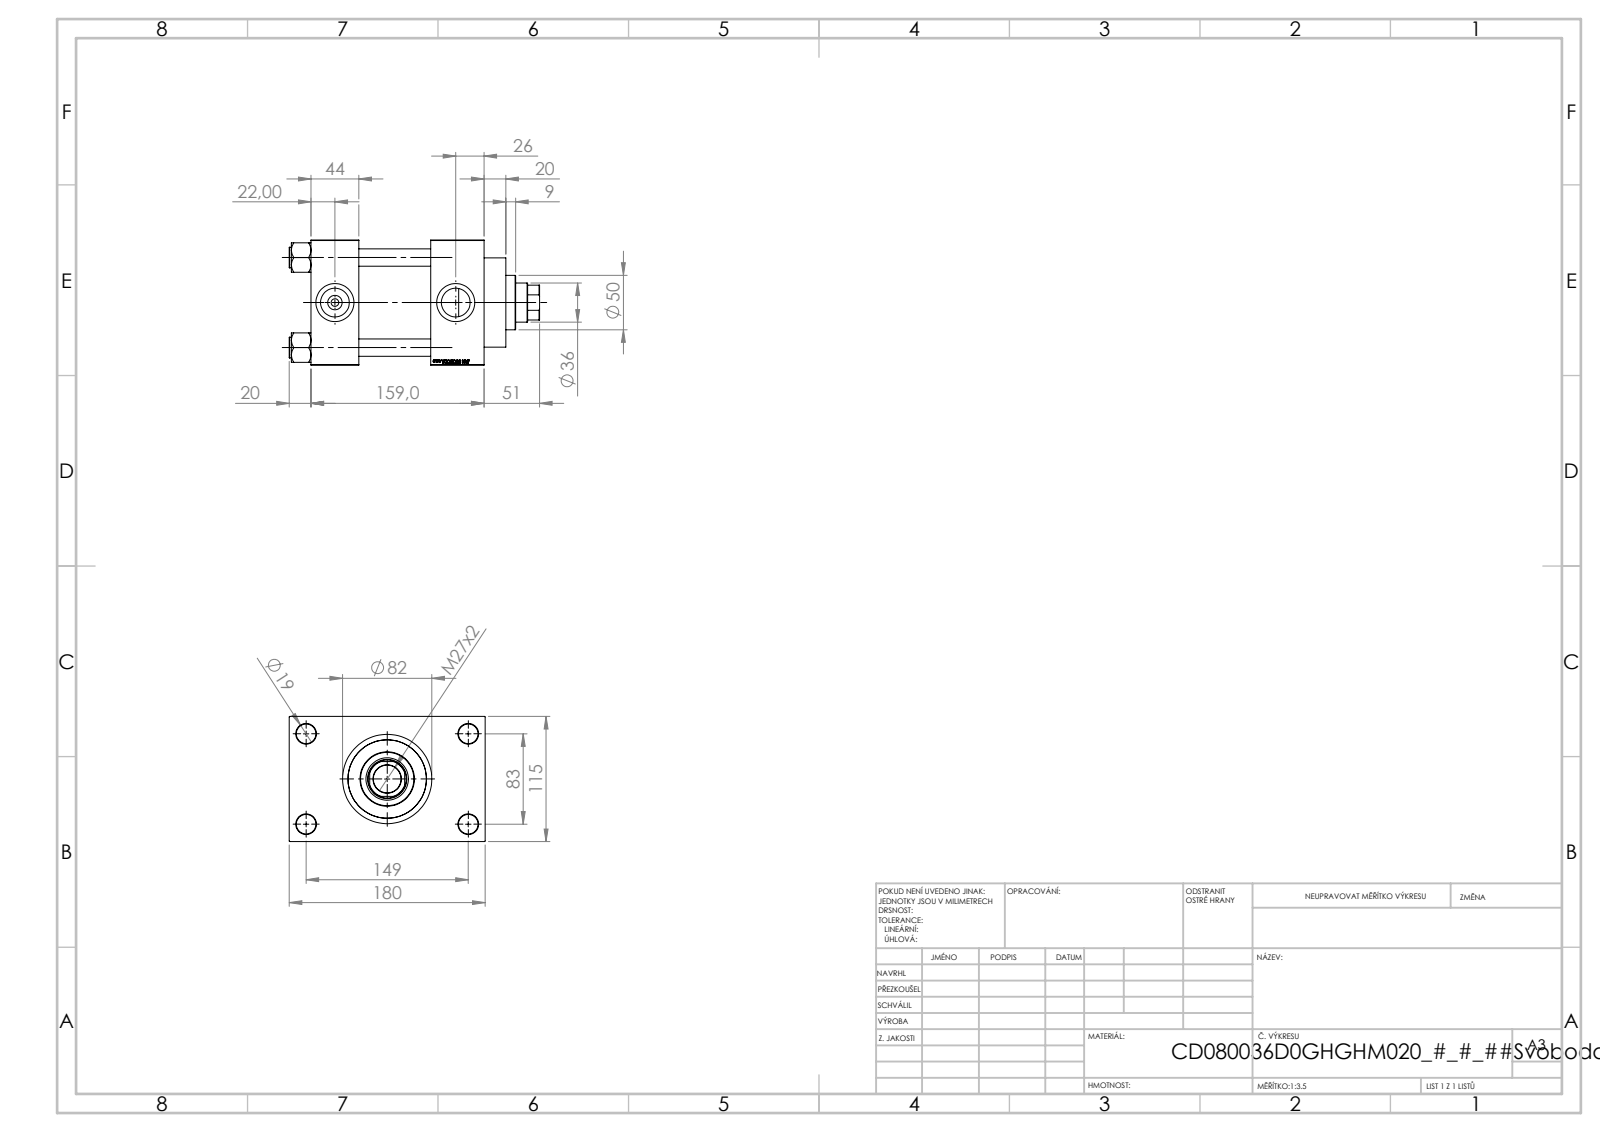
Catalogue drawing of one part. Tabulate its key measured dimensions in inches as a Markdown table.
| quantity | value |
| --- | --- |
| part name | V215CD_D_Body; V215CD_VC_A; V215CD_D_TYCINKA; V215CD_VCP_D (+1 more) |
| STEP written by | SolidWorks 2019 (CONFIG_CONTROL_DESIGN) |
| units | inches |
| bodies | 11 solids, 1151 faces (545 planar, 88 cylindrical, 518 other) |
| overall size | 9.055 × 7.087 × 4.528 |
| volume | 120.8 in³ |
| surface area | 459.7 in² |
| round holes (diameter × count) | 0.63 × 4, 0.709 × 4, 0.276 × 2, 1.041 × 2, 1.378 × 2, 1.004 × 1, 1.417 × 1, 1.535 × 1, 2.402 × 1, 2.835 × 1, 3.15 × 1 |
| round bosses / shafts (diameter × count) | 0.748 × 4, 3.386 × 1, 3.228 × 1, 1.969 × 1 |
| partial cylindrical surfaces (radius × count) | 0.689 × 1 |
| main face-to-face distances | 4.528, 2.598, 4.331, 1.929, 1.732, 6.26, 1.28, 5.807, 0.787, 2.717 |
| hole center spacings | 1.305, 2.302, 3.256, 3.357, 3.513, 4.561, 5.607, 3.268 |
